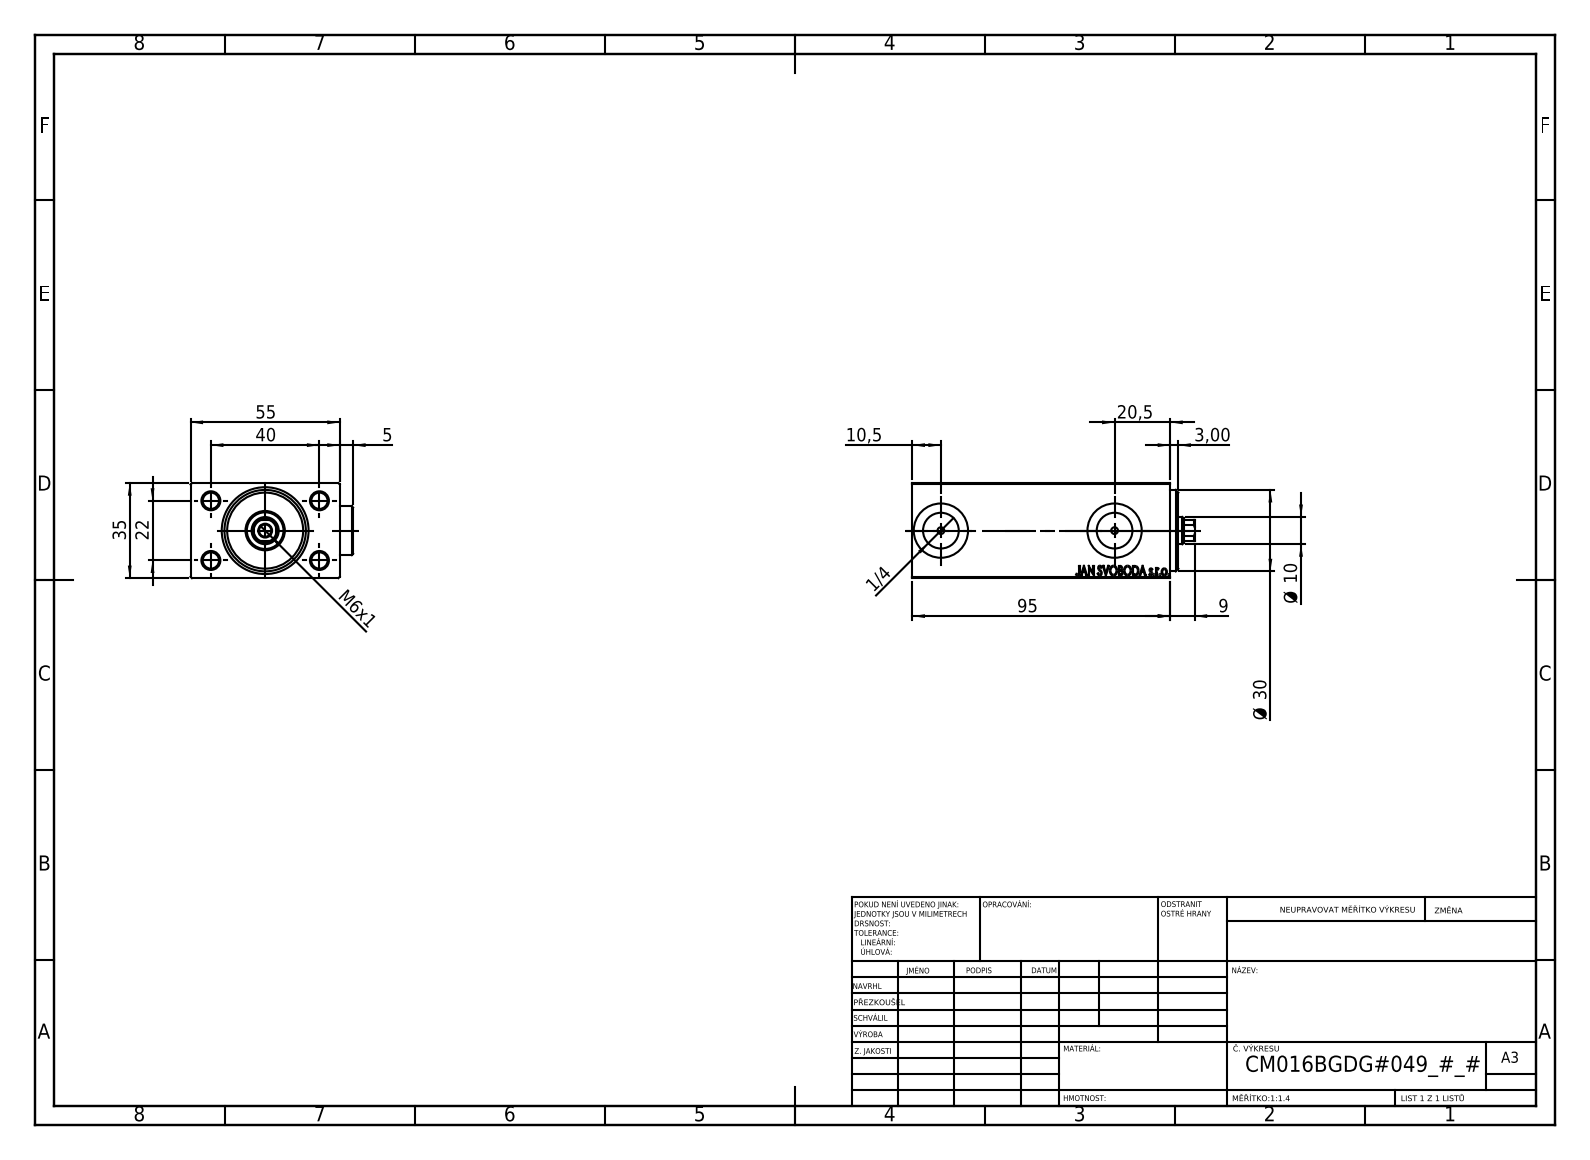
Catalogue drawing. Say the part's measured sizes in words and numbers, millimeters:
The part is named "V450CM_B_VCP; Zatka_OIL_PORT; V450CM_B_Body; V450CM_VC_B". Its 3-D file was written by "SolidWorks 2019 (CONFIG_CONTROL_DESIGN)". It is 5 solids with 935 faces: 435 planar, 70 cylindrical and 430 other. Overall it measures 104 by 59.9 by 35 millimeters. Its volume is 171 502 cubic millimeters and its surface area 38 032 square millimeters. Round holes: 4 of diameter 6, 2 of diameter 2.5, 2 of diameter 13.16, 2 of diameter 20, 1 of diameter 4.5, 1 of diameter 10, 1 of diameter 13.5, 1 of diameter 14.5, 1 of diameter 16, 1 of diameter 18, 1 of diameter 30. Round bosses or shafts: 2 of diameter 18. Partial cylindrical surfaces (rounded edges, fillets, slot ends): 1 of radius 4.5. The main face-to-face distances are 35, 55, 5, 90, 54.9, 95, 3, 8, 98, 54.8. The hole center spacings are 22.83, 22, 40, 45.65, 64.
